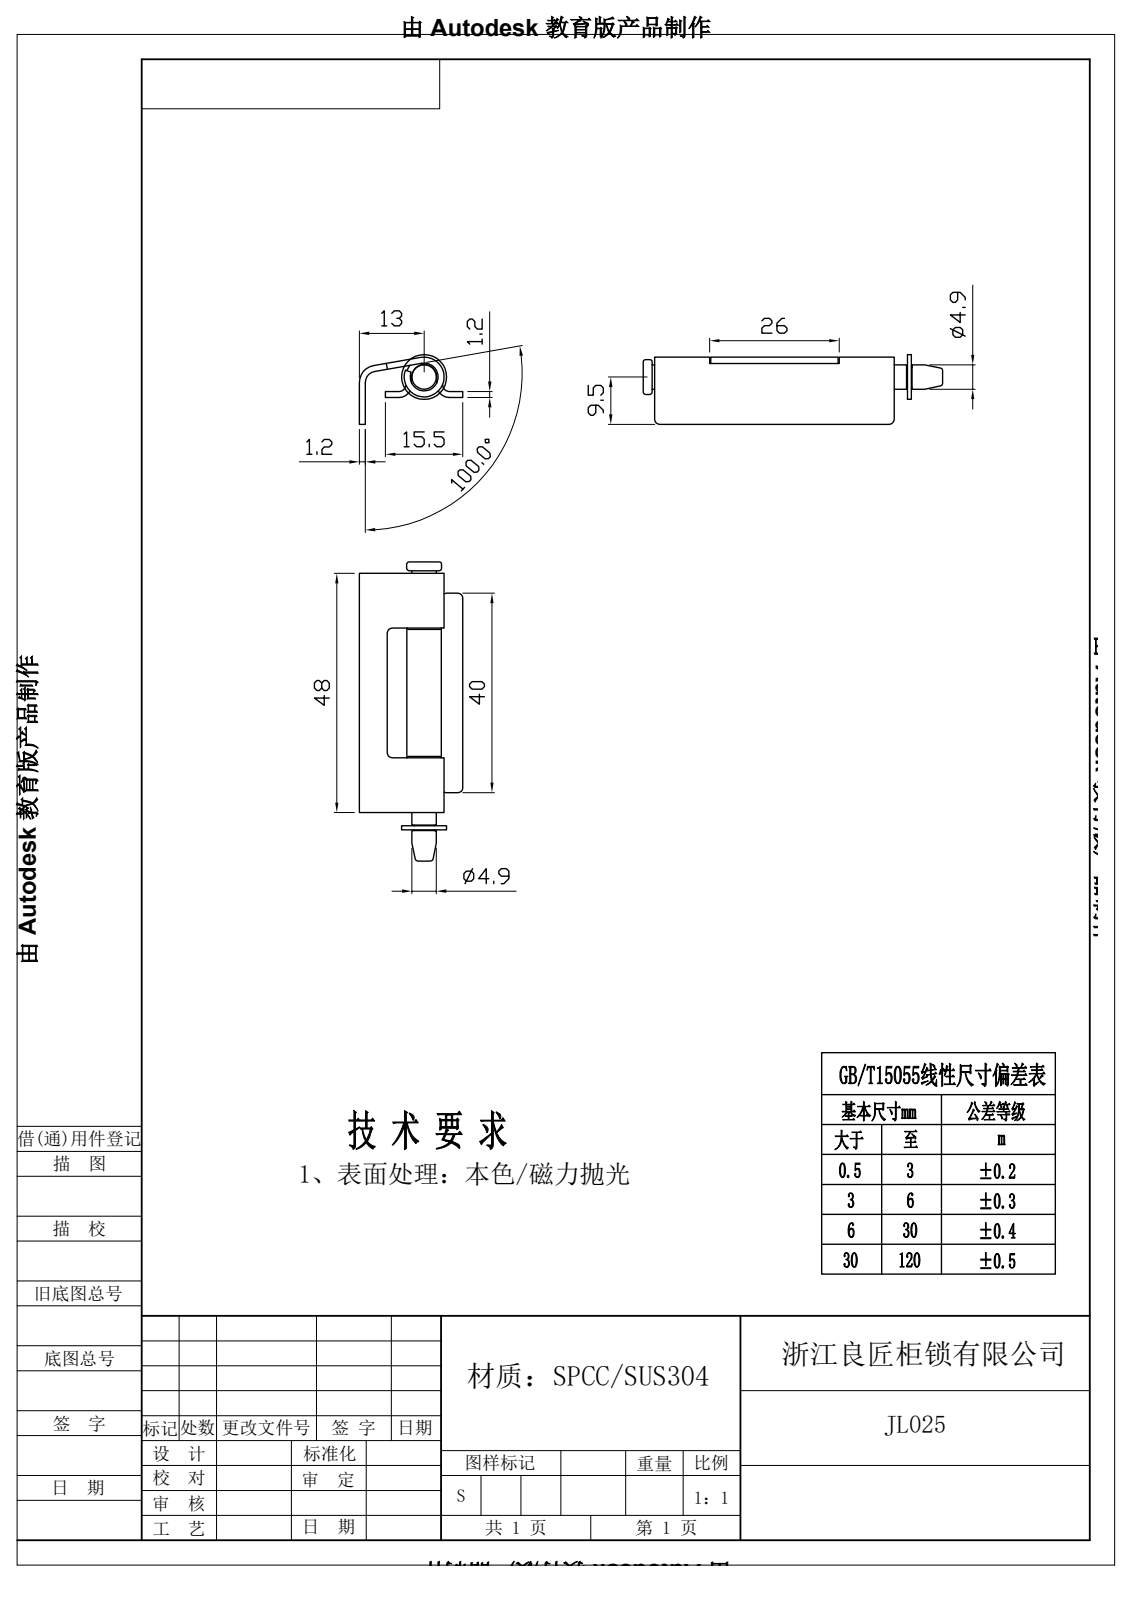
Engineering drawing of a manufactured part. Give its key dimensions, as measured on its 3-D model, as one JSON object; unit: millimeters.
{"step_written_by": "Rhino 8.5 (CONFIG_CONTROL_DESIGN)", "units": "millimeters", "bodies": {"solids": 3, "faces": 87, "planar": 39, "cylindrical": 40, "other": 8}, "overall_size": [60, 20.75, 14], "volume_mm3": 3543, "surface_area_mm2": 5505, "round_holes": [[5.6, 1]], "round_bosses_or_shafts": [[9, 1], [8, 1], [7, 1], [4.9, 1], [4, 1]], "partial_cylinders_radius": [[1, 12], [2.5, 3], [1.3, 2], [2.3, 1], [3.5, 1], [3.7, 1]], "face_to_face_distances": [1.2, 1.21, 11, 37, 5.4, 6.6, 0.8, 51.45, 50.65, 3.45]}
